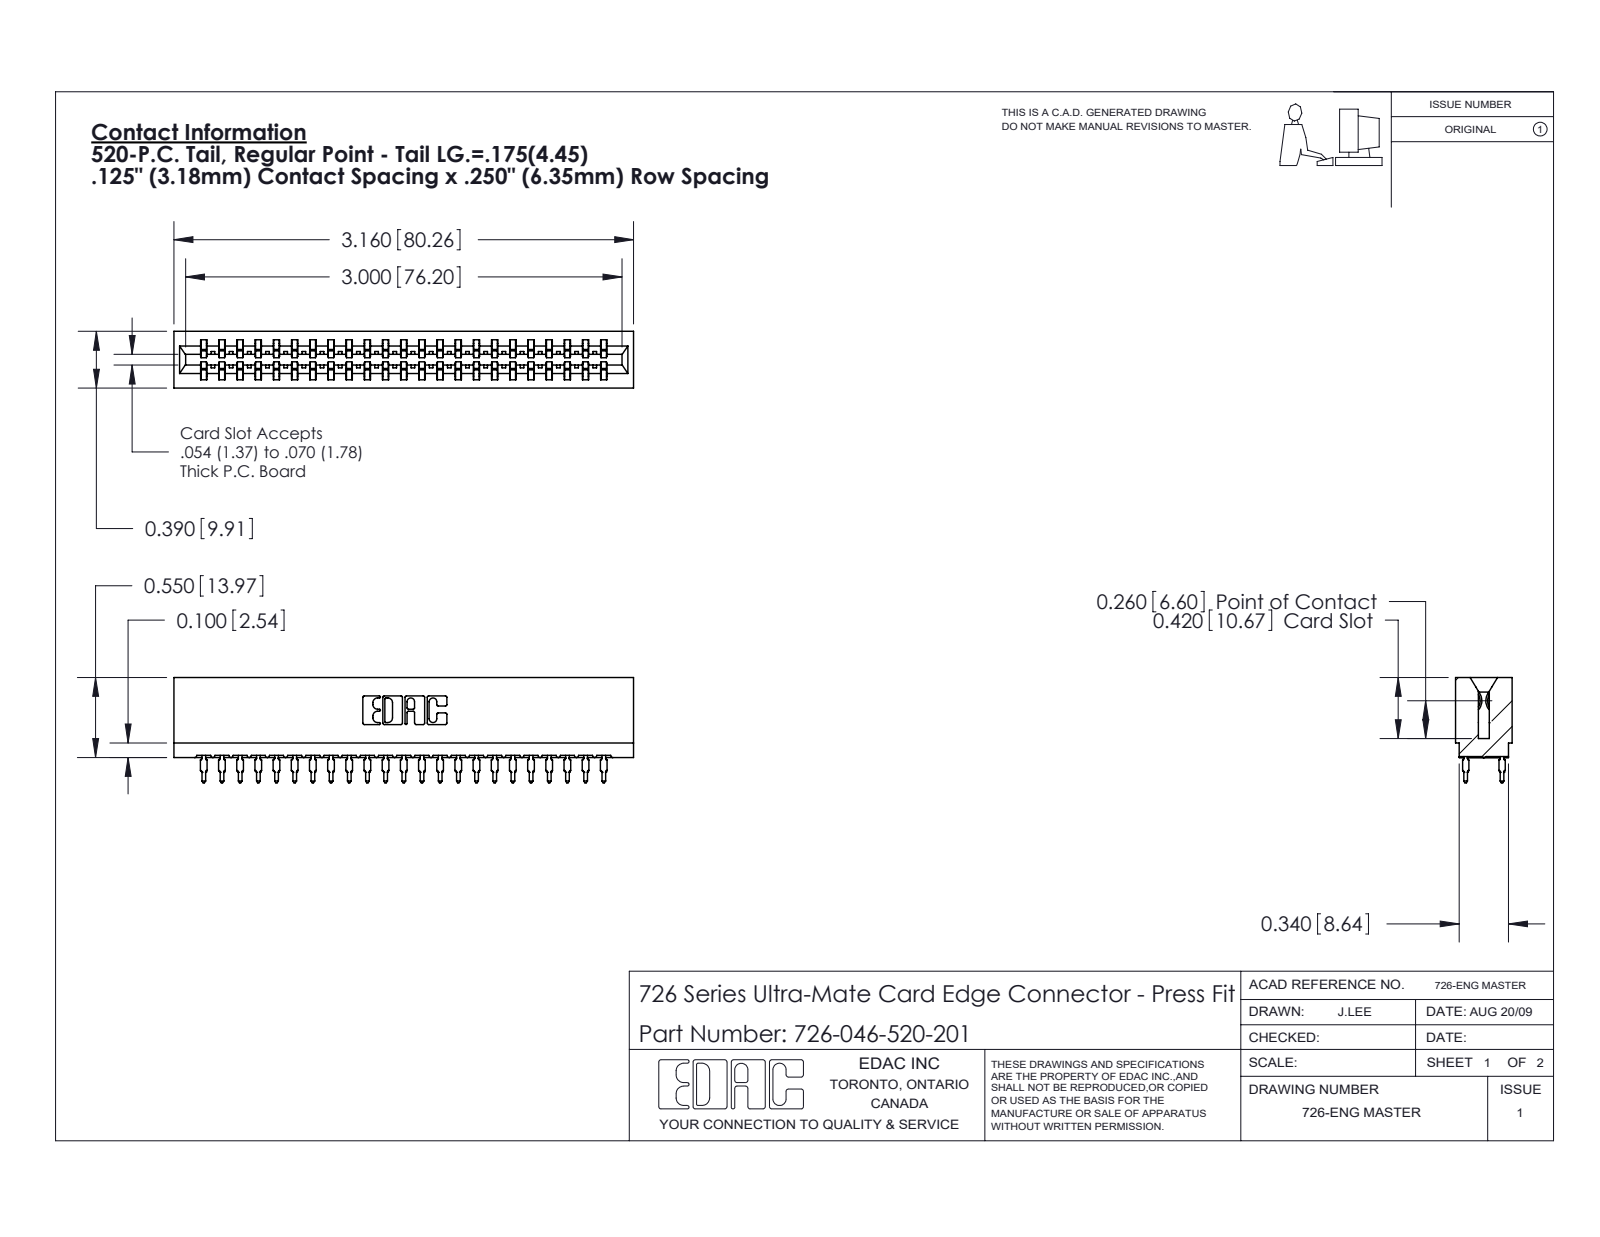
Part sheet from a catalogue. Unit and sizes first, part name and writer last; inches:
Units: inches
Overall size (bounding box): 3.16 × 0.724 × 0.39
Partial cylindrical surfaces — rounded edges, fillets, slot ends (radius × count): R0.021 ×92, R0.015 ×24, R0.01 ×22, R0.005 ×8, R0.011 ×8, R0.007 ×6, R0.031 ×6, R0.026 ×3
Main face-to-face distances: 0.057, 0.333, 0.39, 0.025, 0.307, 0.25, 0.275, 0.75, 0.083, 0.042
Volume: 0.454 in³ · Surface area: 18.41 in²
Bodies: 47 solids, 4214 faces (2171 planar, 847 cylindrical, 1196 other)
Part name (STEP PRODUCT): 726 Part_.515 Slot Depth - 01; 726-046-520-201; 746-292-001_520
STEP written by: SolidWorks 2020 (CONFIG_CONTROL_DESIGN)
